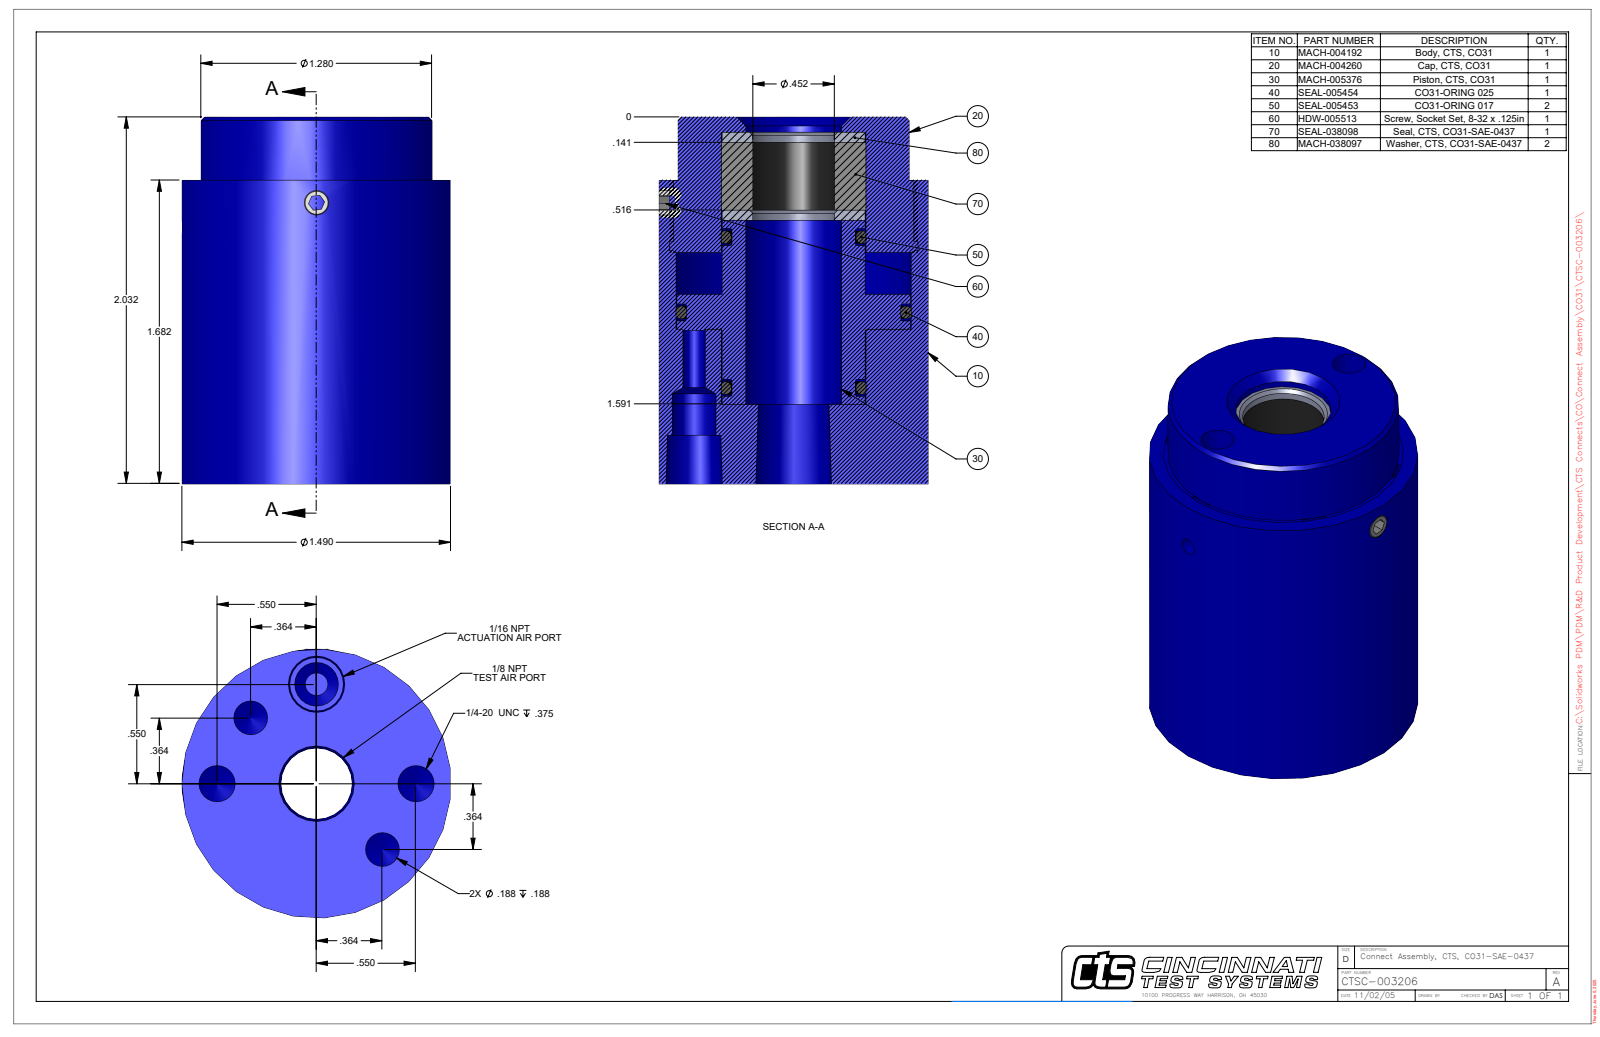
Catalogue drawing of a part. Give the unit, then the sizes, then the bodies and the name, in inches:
Units: inches
Overall size (bounding box): 2.032 × 1.49 × 1.49
Round holes (diameter × count): ⌀0.187 ×4, ⌀0.201 ×2, ⌀0.094 ×1, ⌀0.136 ×1, ⌀0.242 ×1, ⌀0.452 ×1, ⌀0.53 ×1, ⌀0.8 ×1, ⌀1.33 ×1
Round bosses / shafts (diameter × count): ⌀1.49 ×1, ⌀1.28 ×1, ⌀0.79 ×1
Partial cylindrical surfaces — rounded edges, fillets, slot ends (radius × count): R0.687 ×1, R0.735 ×1
Main face-to-face distances: 2.032, 1.682, 0.35, 0.344, 1.338, 1.688, 0.441, 0.097, 1.241, 1.591
Hole centre spacings: 0.515, 0.409, 0.55, 0.984, 0.035, 0.394, 0.754, 0.778
Volume: 2.935 in³ · Surface area: 17.21 in²
Bodies: 1 solid, 108 faces (52 planar, 38 cylindrical, 18 other)
Part name (STEP PRODUCT): CTSC-003206
STEP written by: SolidWorks 2023 (AUTOMOTIVE_DESIGN)
